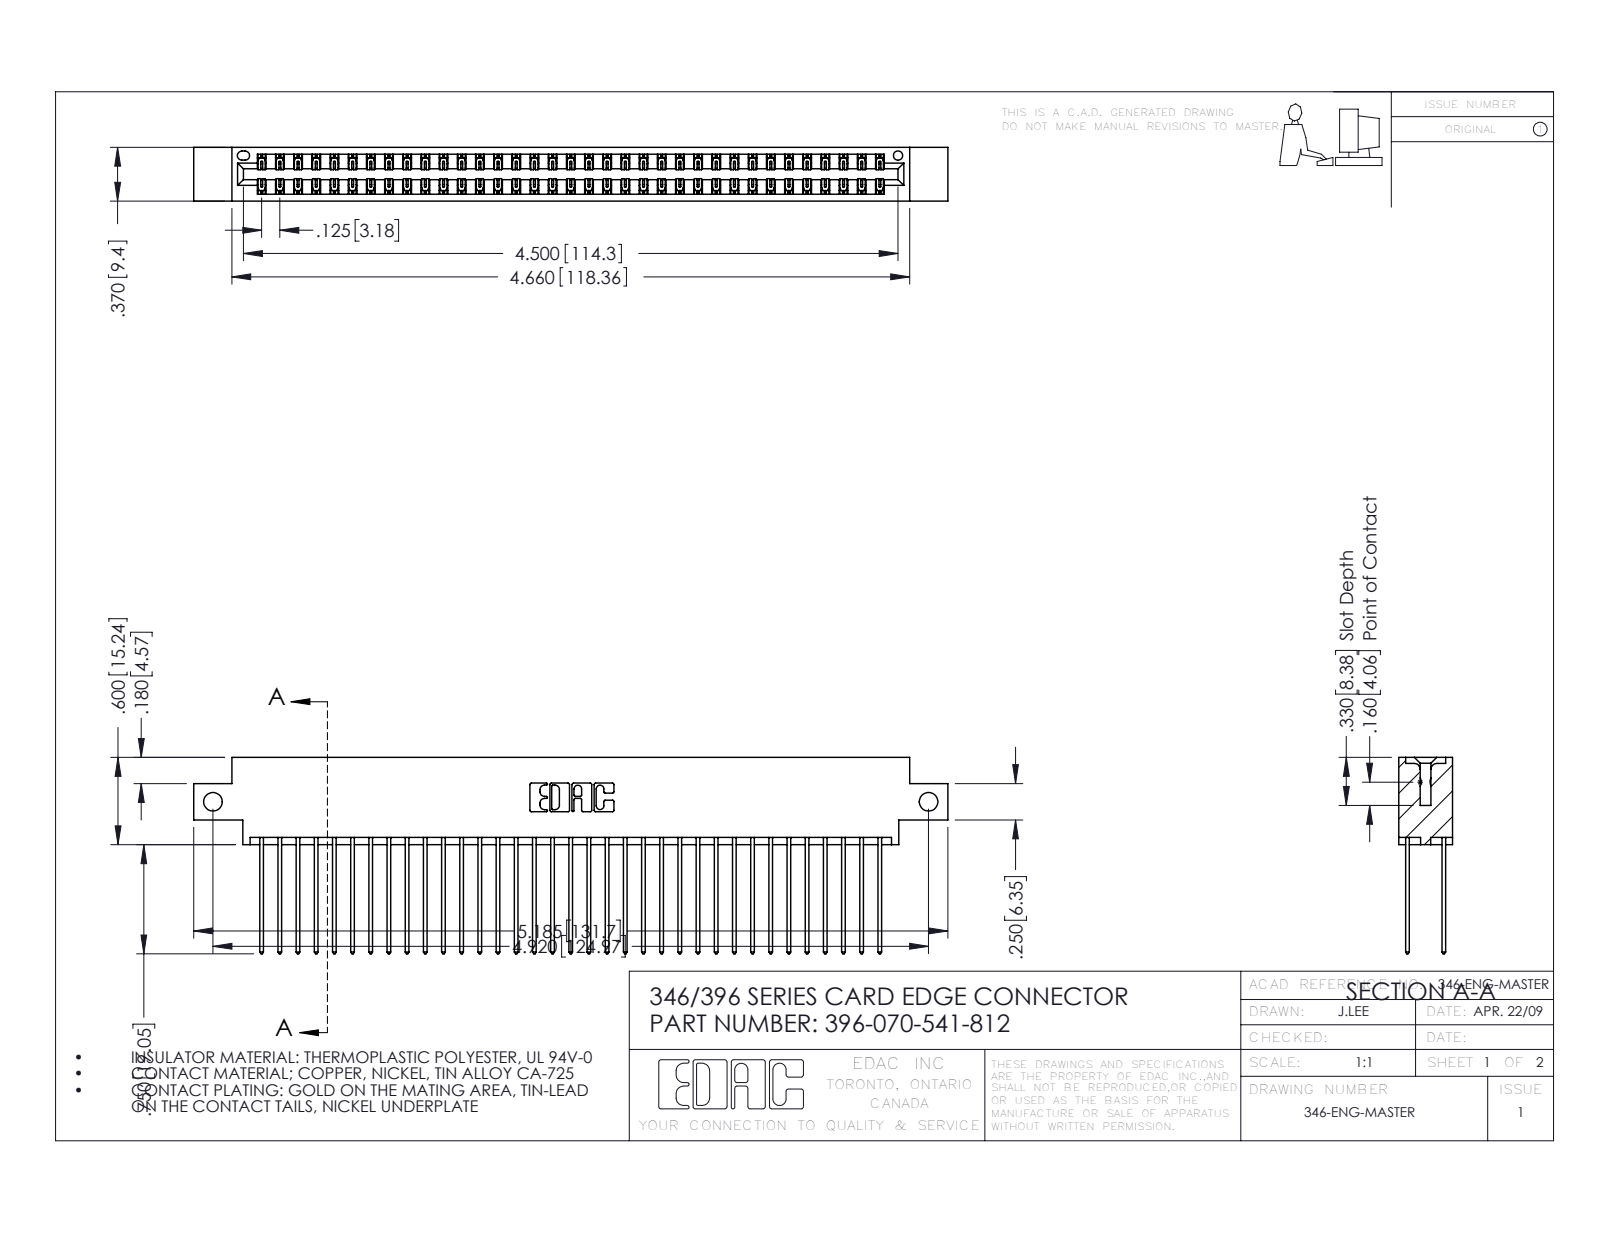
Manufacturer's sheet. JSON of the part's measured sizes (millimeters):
{"part_name": "396-070-541-812; 345-292-001_345-293-141; 346 Part_0.170 Offset - Side Mount", "step_written_by": "SolidWorks 2016 (CONFIG_CONTROL_DESIGN)", "units": "millimeters", "bodies": {"solids": 71, "faces": 3766, "planar": 2530, "cylindrical": 1236, "other": 0}, "overall_size": [131.7, 34.3, 9.4], "volume_mm3": 12900, "surface_area_mm2": 19660, "round_holes": [[3.3, 2], [1.6, 1]], "partial_cylinders_radius": [[0.2, 105], [0.3, 70], [0.3, 22], [0.2, 6], [0.8, 6], [0.7, 3], [0.4, 2], [0.6, 2]], "face_to_face_distances": [1.2, 8.2, 6.4, 1.8, 7.6, 0.6, 9.4, 7, 5.7, 3.8], "hole_center_spacings": [125]}
